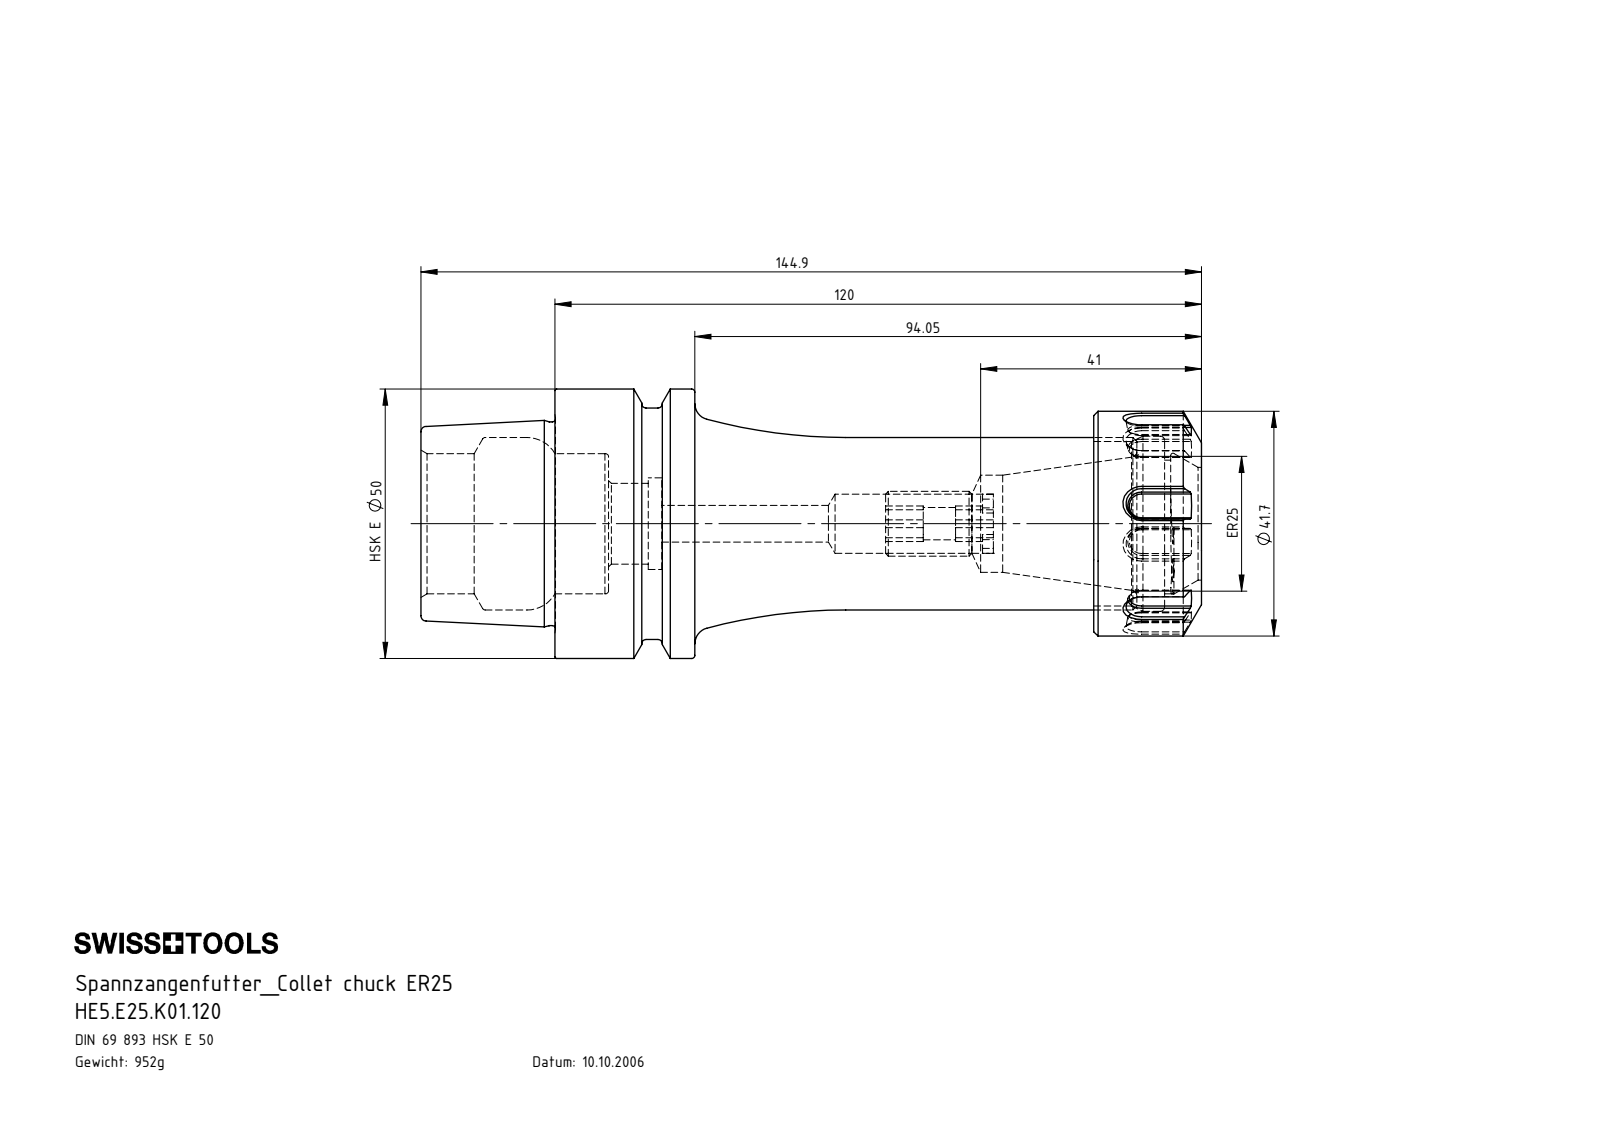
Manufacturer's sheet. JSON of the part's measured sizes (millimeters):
{"part_name": "HE5-E25.K01.120_A_Fertigbearbeitung; HE5.E25.K01.120; ERU-AN5.K01.020_A; E25-ER1.001.020", "step_written_by": "SolidWorks 2017 (CONFIG_CONTROL_DESIGN)", "units": "millimeters", "bodies": {"solids": 3, "faces": 226, "planar": 92, "cylindrical": 43, "other": 91}, "overall_size": [144.9, 50, 50], "volume_mm3": 121282, "surface_area_mm2": 33732, "round_holes": [[6, 1], [6.8, 1], [11, 1], [15, 1], [17, 1], [18, 1], [20.9, 1], [26, 1], [30.5, 1], [32, 1], [32.5, 1]], "round_bosses_or_shafts": [[50, 1], [42.95, 1], [41.7, 1], [37.81, 1], [12, 1]], "partial_cylinders_radius": [[12.17, 2]], "face_to_face_distances": [100, 20, 120, 24.9, 124.9, 144.9, 50.85, 25.95, 74.05, 94.05]}
